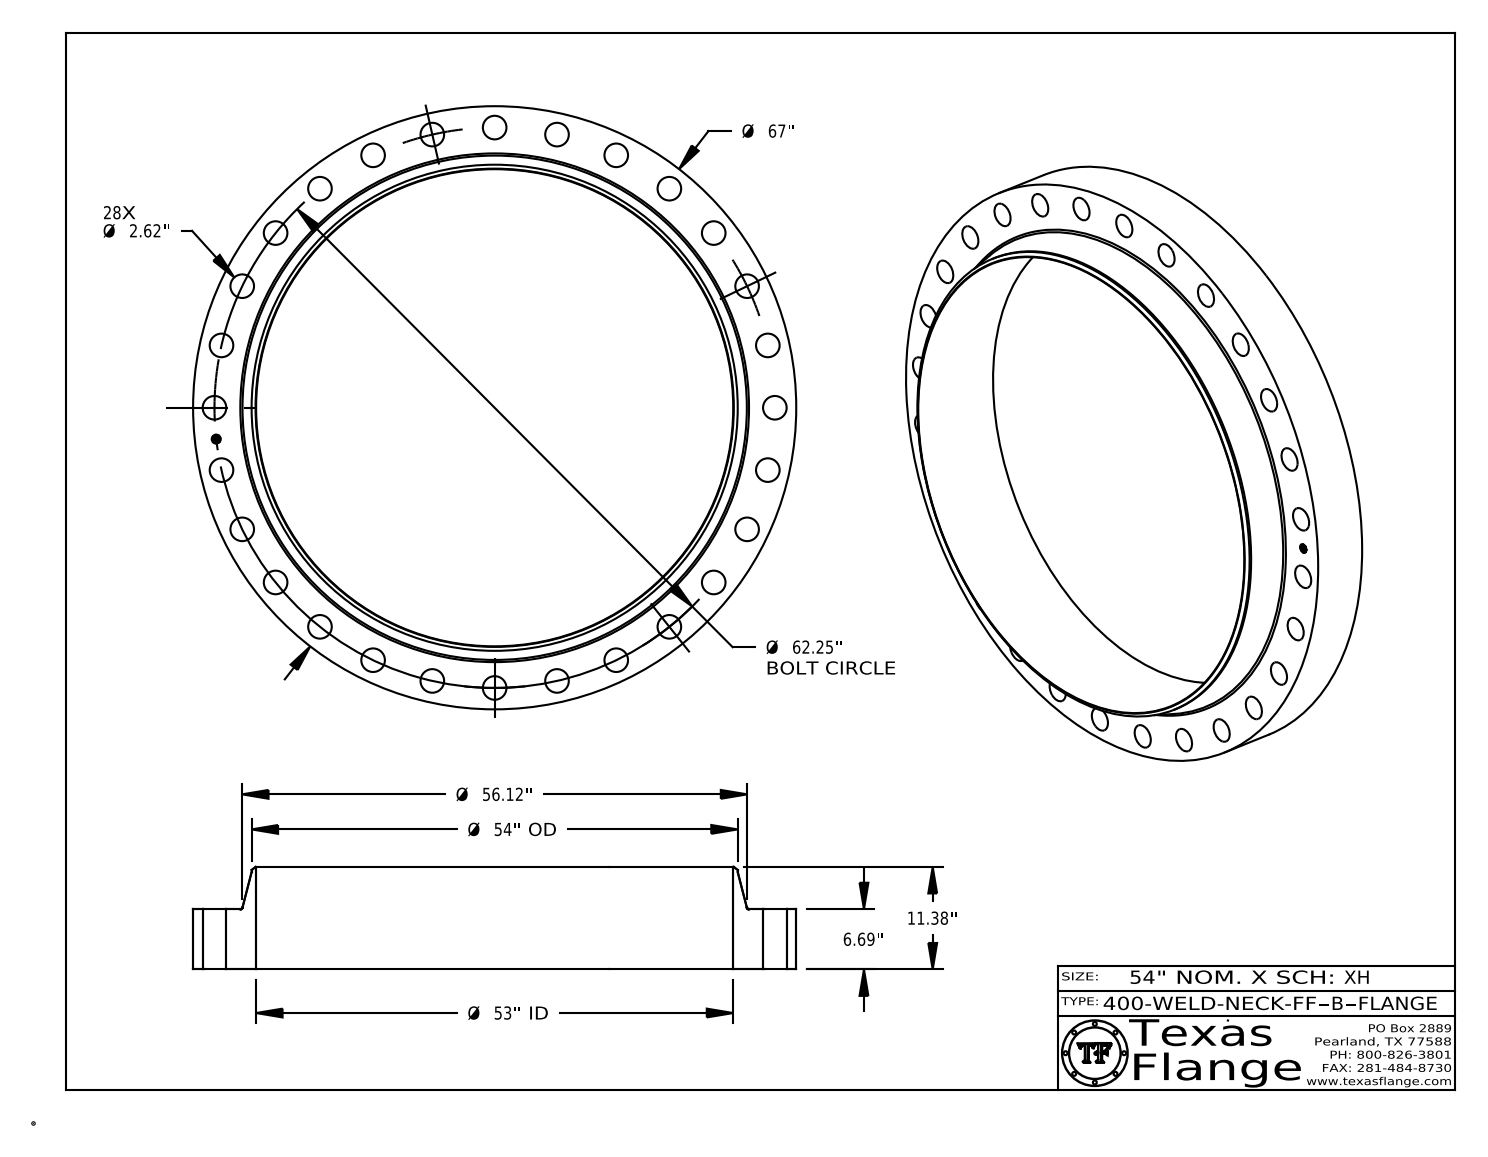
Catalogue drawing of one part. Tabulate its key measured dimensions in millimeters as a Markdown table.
| quantity | value |
| --- | --- |
| part name | 400-WELD-NECK-FF, Series B |
| STEP written by | CATIA V5 STEP AP214 (AUTOMOTIVE_DESIGN) |
| units | millimeters |
| bodies | 1 solid, 456 faces (368 planar, 82 cylindrical, 6 other) |
| overall size | 1701.8 × 1701.8 × 289.1 |
| volume | 140 500 000 mm³ |
| surface area | 5 021 000 mm² |
| round holes (diameter × count) | 66.5 × 28, 25.4 × 1, 1346.2 × 1 |
| round bosses / shafts (diameter × count) | 1.5 × 8, 1701.8 × 1, 1371.6 × 1, 20 × 1 |
| main face-to-face distances | 169.9, 289.1, 119.1, 0.4, 169.5, 119.5, 7.6, 7.4, 1.4, 4.9 |
| hole center spacings | 177, 985.8, 1236.2, 1338.8, 1541.5, 351.8, 686, 841.2 |
